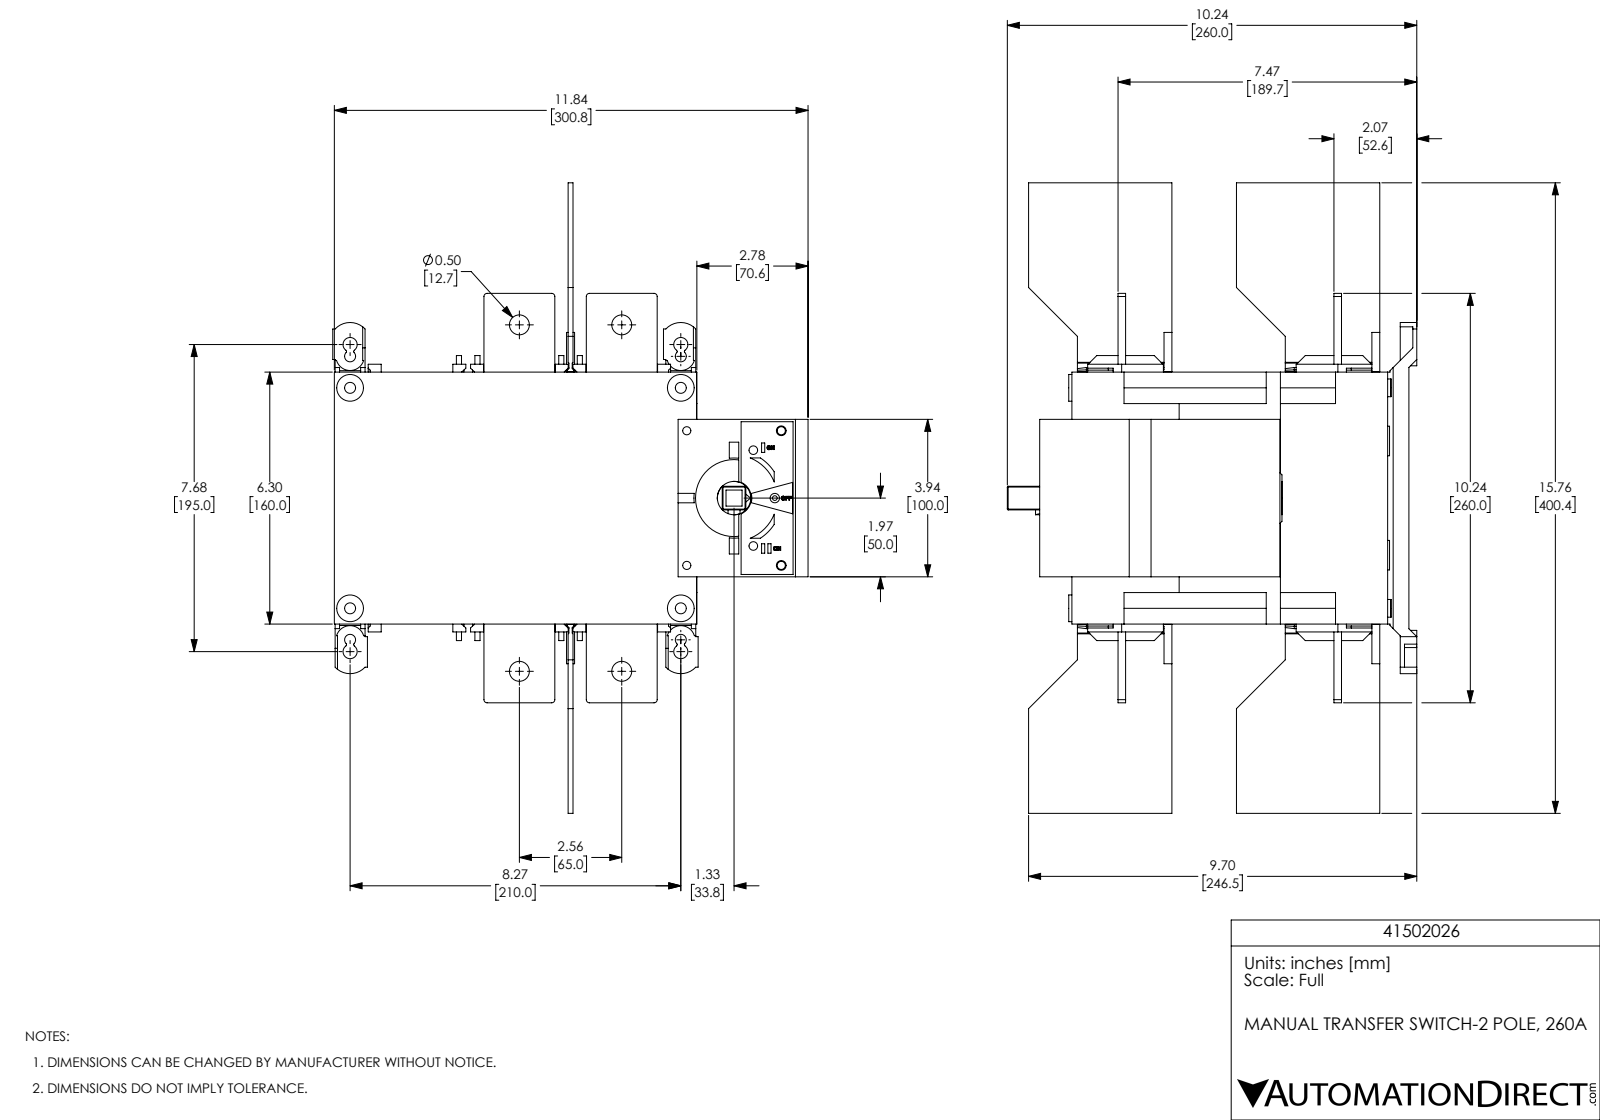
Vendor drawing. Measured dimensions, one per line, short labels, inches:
name: 41502026
written by: SolidWorks 2017 (AUTOMOTIVE_DESIGN)
unit: in
bodies: 7 solids, 1348 faces (1066 planar, 276 cylindrical, 6 other)
size: 15.764 × 11.882 × 10.236
volume: 482 in³; area: 850.2 in²
holes: 12× ⌀0.248, 4× ⌀0.205, 4× ⌀0.276, 4× ⌀0.354, 4× ⌀0.472, 4× ⌀0.5, 2× ⌀0.217, 1× ⌀0.118, 1× ⌀0.839, 1× ⌀0.846
bosses: 4× ⌀0.669, 1× ⌀0.833, 1× ⌀0.236
rounds: 12× R0.344, 8× R0.039, 8× R0.079, 8× R0.217, 4× R0.02, 4× R0.049, 4× R0.138, 4× R0.236
face distances: 0.122, 6.299, 7.894, 5.844, 5.967, 9.055, 3.211, 3.089, 0.189, 1.154
hole spacings: 2.559, 8.268, 2.056, 8.655, 1.083, 1.291, 1.476, 4.035
